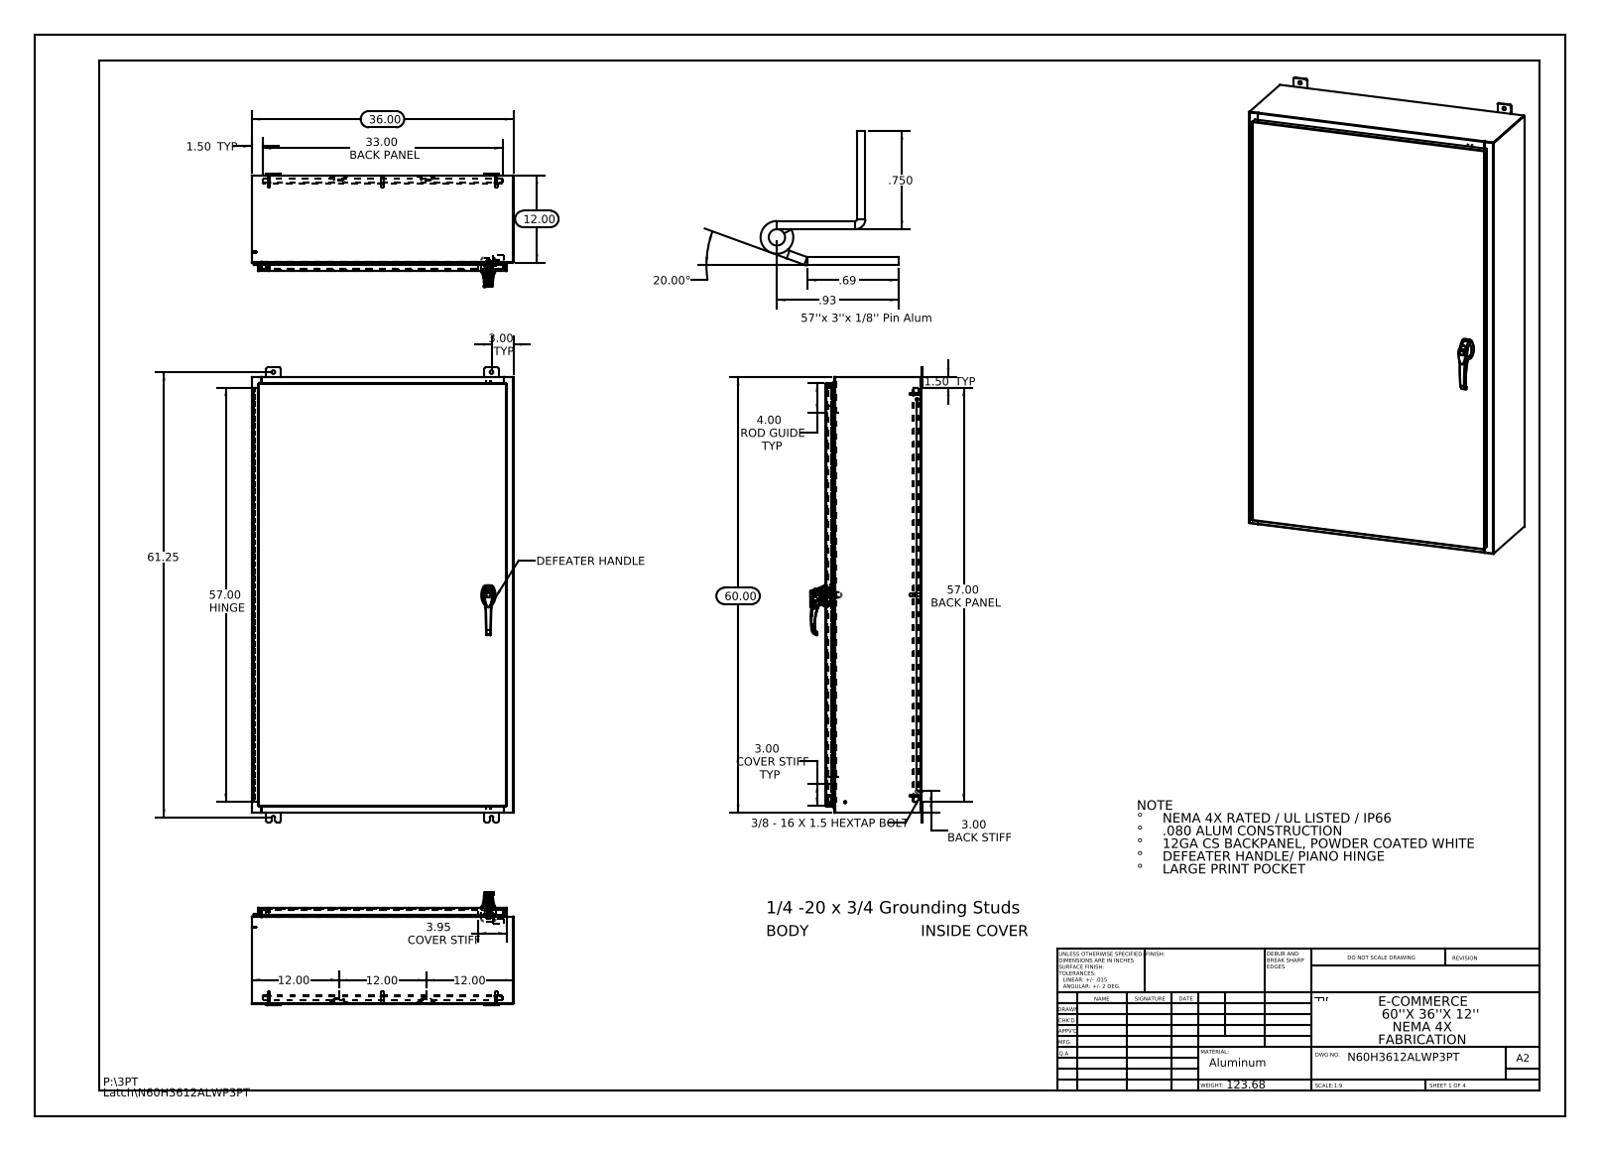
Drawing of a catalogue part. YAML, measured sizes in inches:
part_name: "N60H3612ALWP3PT Hinge Enclosure Side2; N60H3612ALWP3PT Defeater Handle - 3 - 2500-51 ZN; N60H3612ALWP3PT Hinge Cover Side; N60H3612ALWP3PT Mounting Feet (+8 more)"
step_written_by: "SolidWorks 2013 (CONFIG_CONTROL_DESIGN)"
units: inches
bodies: {solids: 51, faces: 3688, planar: 1453, cylindrical: 1449, other: 786}
overall_size: [62.5, 36, 15.495]
volume: 798.5
surface_area: 19824
round_holes:
  - {diameter: 0.5, count: 12}
  - {diameter: 0.25, count: 10}
  - {diameter: 0.138, count: 3}
  - {diameter: 0.161, count: 3}
  - {diameter: 0.079, count: 2}
  - {diameter: 0.203, count: 2}
  - {diameter: 0.313, count: 2}
  - {diameter: 0.437, count: 2}
  - {diameter: 0.125, count: 1}
  - {diameter: 0.125, count: 1}
  - {diameter: 0.197, count: 1}
  - {diameter: 0.276, count: 1}
round_bosses_or_shafts:
  - {diameter: 0.157, count: 10}
  - {diameter: 0.14, count: 10}
  - {diameter: 0.625, count: 8}
  - {diameter: 0.375, count: 8}
  - {diameter: 0.33, count: 8}
  - {diameter: 0.315, count: 3}
  - {diameter: 0.236, count: 3}
  - {diameter: 1.181, count: 1}
partial_cylinders:
  - {radius: 0.118, count: 37}
  - {radius: 0.013, count: 34}
  - {radius: 0.006, count: 33}
  - {radius: 0.088, count: 28}
  - {radius: 0.19, count: 24}
  - {radius: 0.039, count: 15}
  - {radius: 0.028, count: 12}
  - {radius: 0.008, count: 6}
face_to_face_distances: [0.075, 13.126, 13.051, 0.104, 13.201, 1, 12.126, 1.075, 12.051, 1.179]
hole_center_spacings: [23.354, 25.662, 27.625, 41.709, 57.417, 30.975, 31.25, 55.25]
